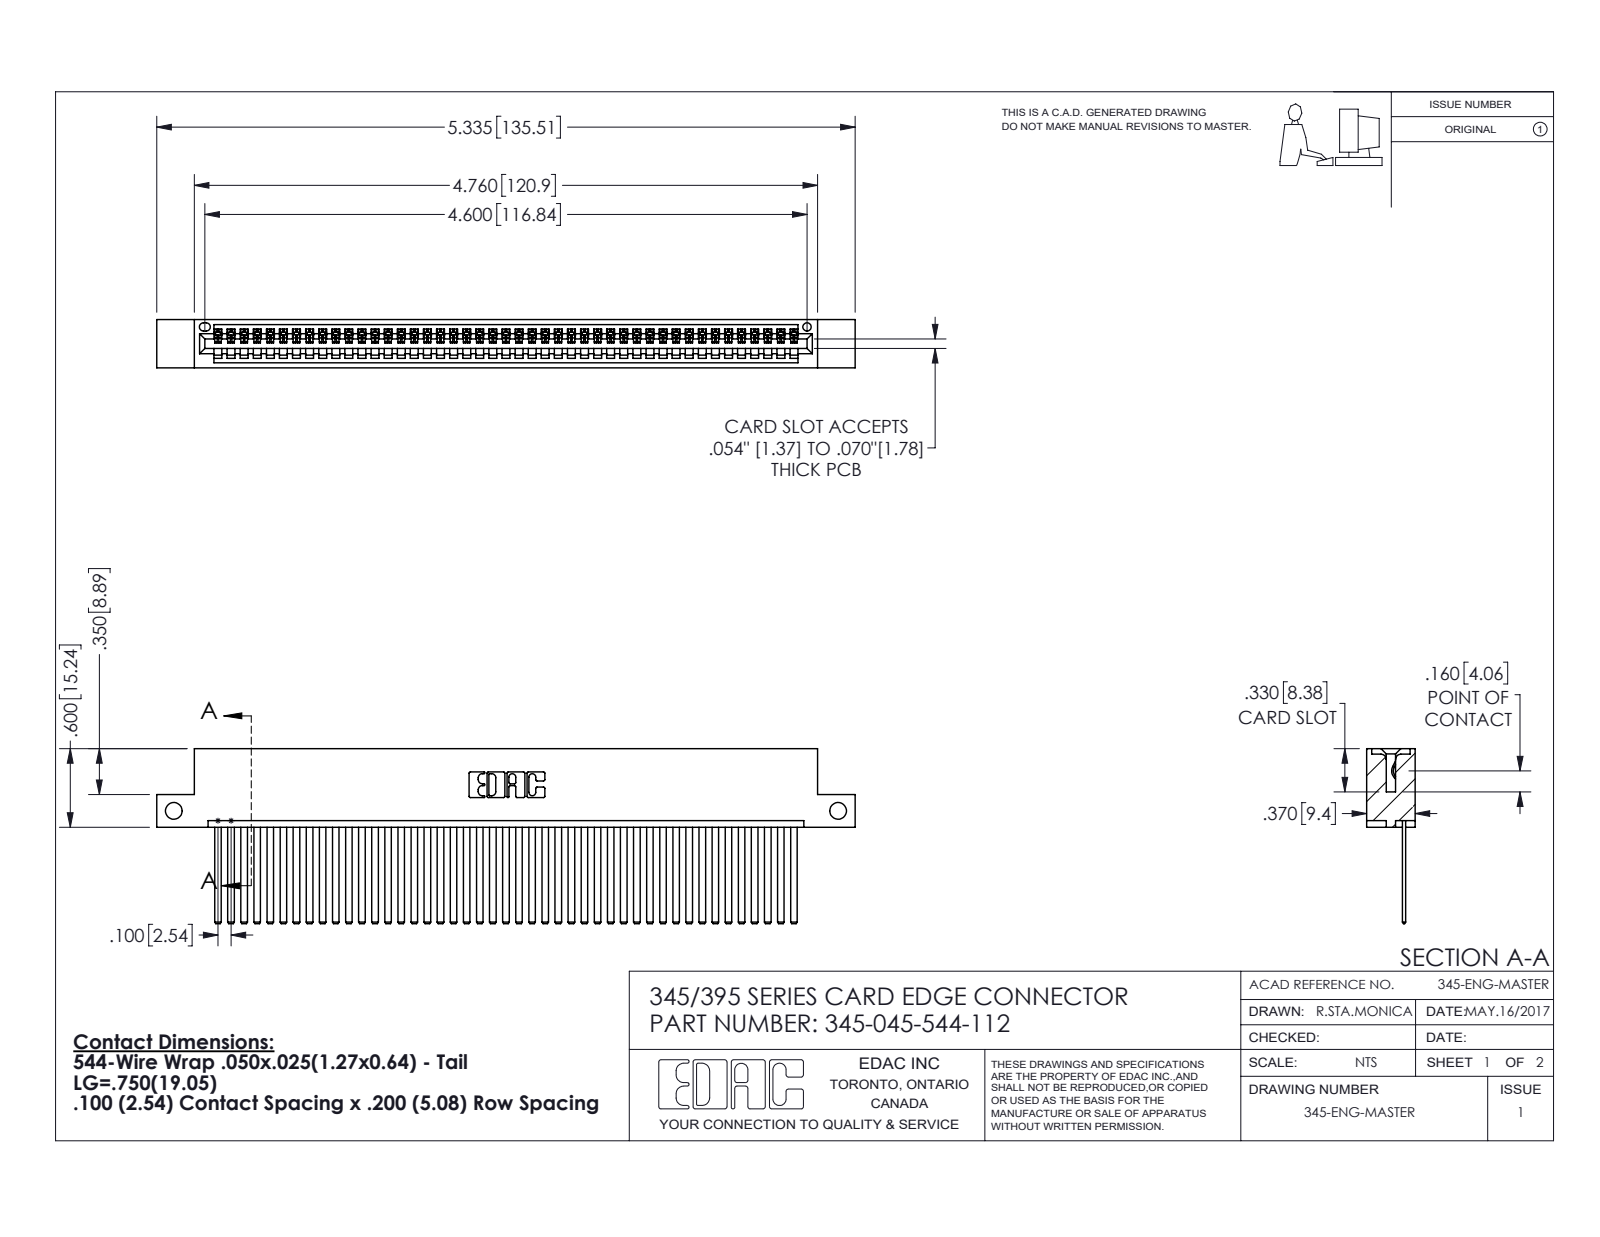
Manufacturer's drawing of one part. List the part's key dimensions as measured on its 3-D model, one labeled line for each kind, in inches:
Part name (STEP PRODUCT): 345-292-001_345-293-144; 345-045-544-112; 345 Part_Flush Mounting Lugs - Side Mount
STEP written by: SolidWorks 2016 (CONFIG_CONTROL_DESIGN)
Units: inches
Bodies: 46 solids, 2466 faces (1700 planar, 766 cylindrical, 0 other)
Overall size (bounding box): 5.335 × 1.337 × 0.37
Volume: 0.813 in³ · Surface area: 29.72 in²
Round holes (diameter × count): ⌀0.128 ×2, ⌀0.064 ×1
Partial cylindrical surfaces — rounded edges, fillets, slot ends (radius × count): R0.006 ×90, R0.01 ×22, R0.007 ×6, R0.031 ×6, R0.026 ×3, R0.031 ×2, R0.04 ×2, R0.014 ×1
Main face-to-face distances: 0.072, 0.298, 0.025, 0.098, 0.272, 0.37, 0.2, 0.225, 0.149, 0.072
Hole centre spacings: 5.075
